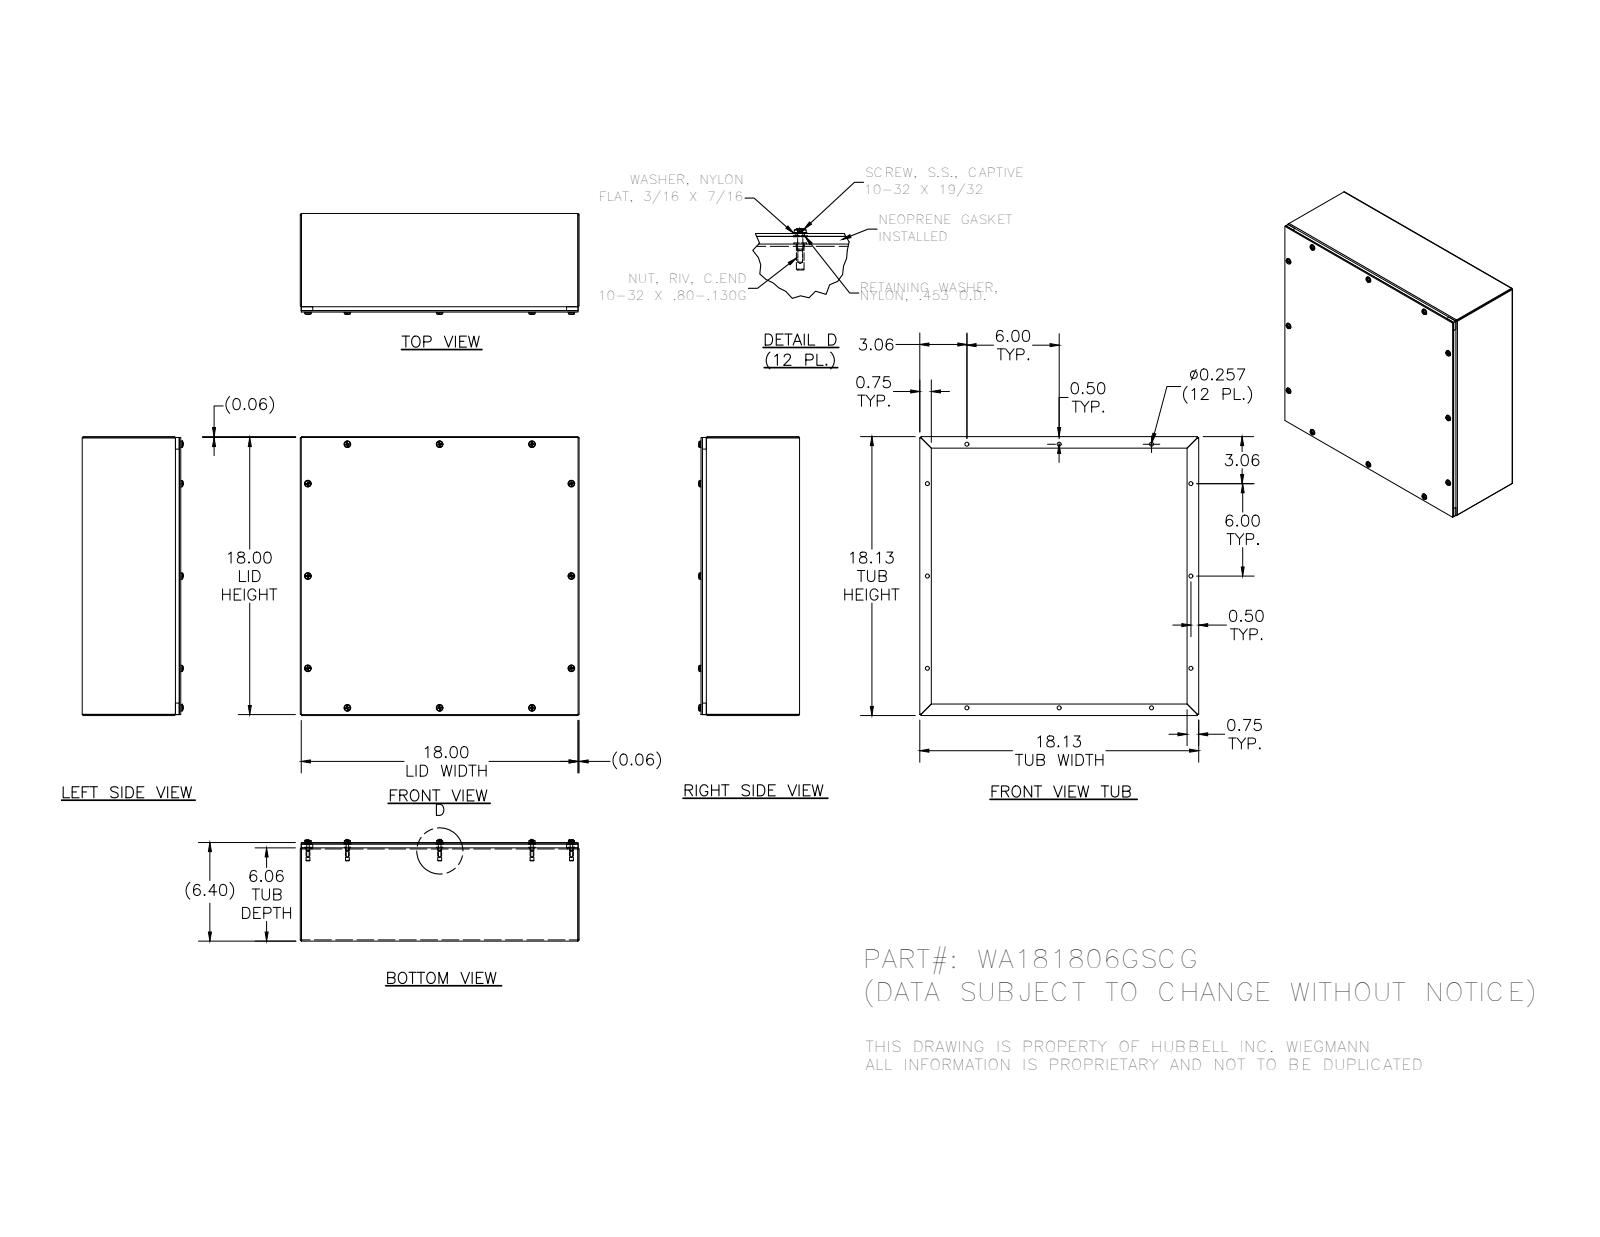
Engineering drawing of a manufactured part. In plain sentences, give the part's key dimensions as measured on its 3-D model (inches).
The part is named "WA181806GSCGBKP; 34984; 37210; 39035 (+3 more)". Its 3-D file was written by "SolidWorks 2014 (AUTOMOTIVE_DESIGN)". It is 54 solids with 1264 faces: 596 planar, 328 cylindrical and 340 other. Overall it measures 18.125 by 18.125 by 6.558 inches. Its volume is 103.9 cubic inches and its surface area 2 444 square inches. Round holes: 12 of diameter 0.156, 12 of diameter 0.188, 12 of diameter 0.196, 12 of diameter 0.257, 12 of diameter 0.278, 12 of diameter 0.281. Round bosses or shafts: 12 of diameter 0.453, 12 of diameter 0.437, 12 of diameter 0.406, 12 of diameter 0.248, 12 of diameter 0.167. Partial cylindrical surfaces (rounded edges, fillets, slot ends): 12 of radius 0.089, 8 of radius 0.016, 8 of radius 0.09. The main face-to-face distances are 0.074, 0.094, 6.33, 6.404, 6.236, 6.31, 18.051, 17.977, 5.986, 18.125. The hole center spacings are 6, 18.146, 12, 8.937, 16.893, 14.785, 14.786, 16.893.
